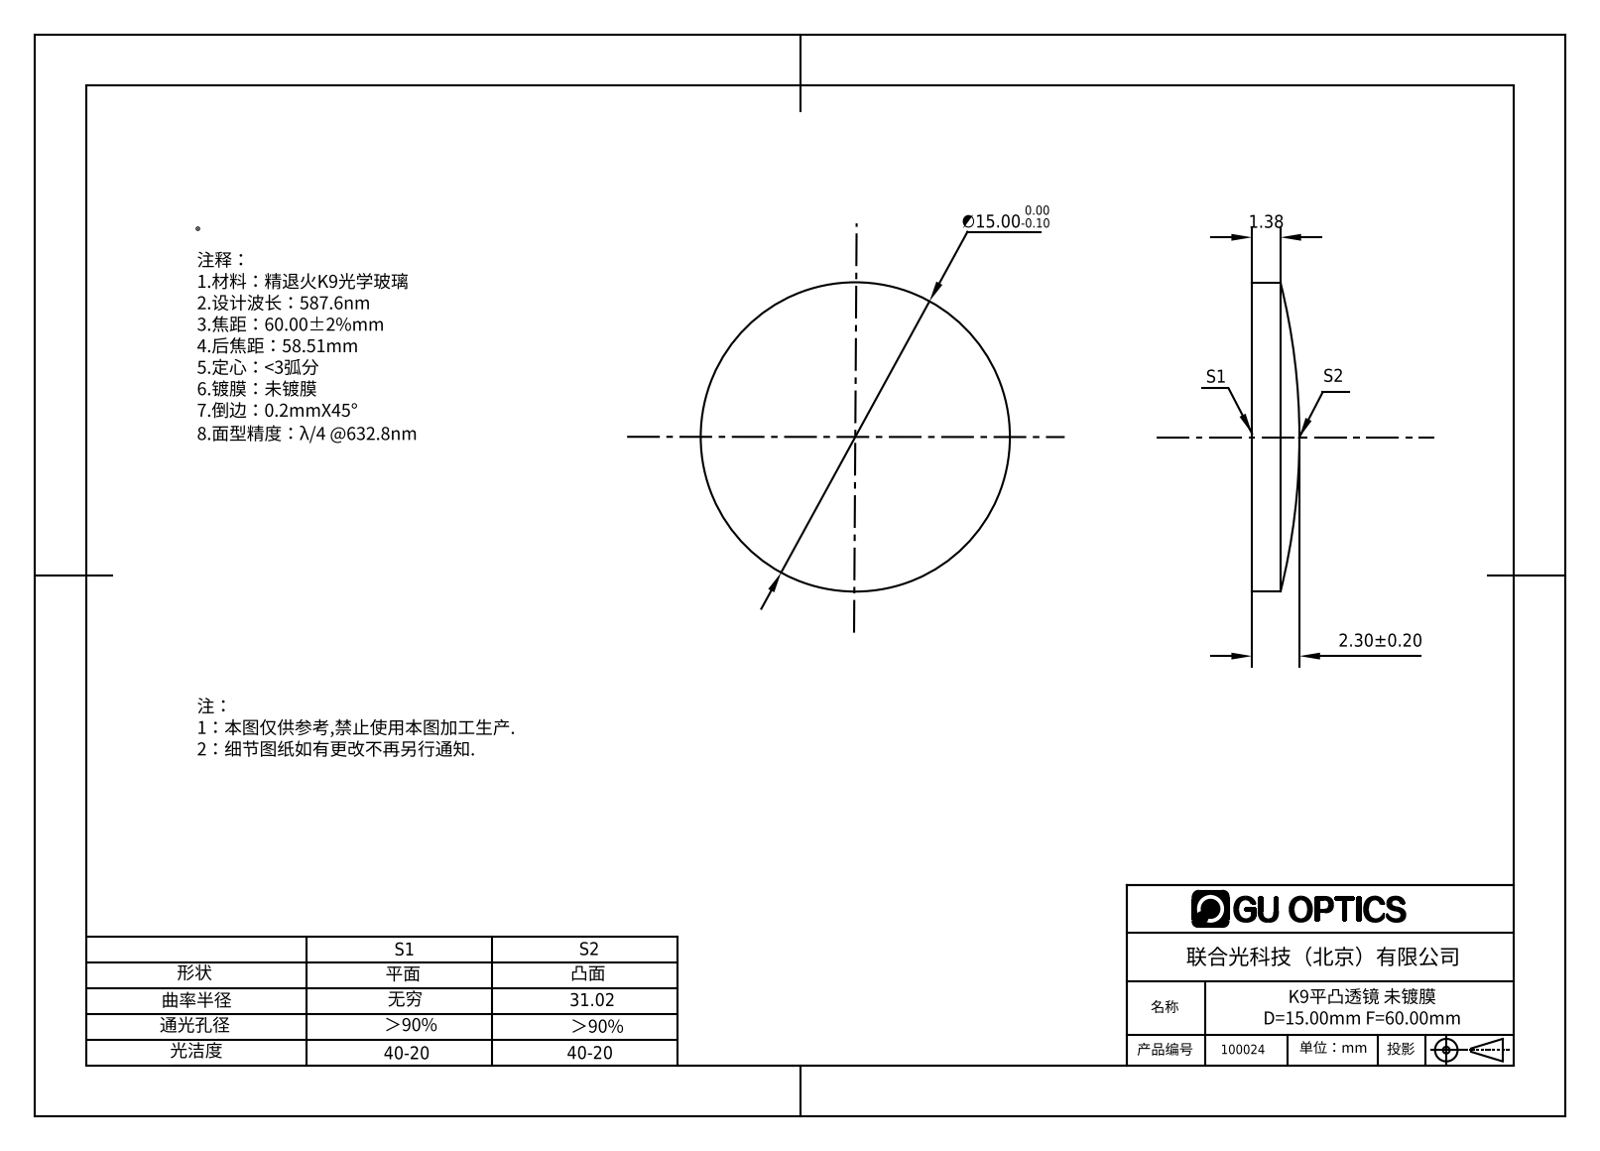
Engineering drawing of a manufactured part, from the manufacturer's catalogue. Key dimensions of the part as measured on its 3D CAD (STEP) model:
Part name (STEP PRODUCT): 100024
STEP written by: SolidWorks 2016 (AUTOMOTIVE_DESIGN)
Units: millimetres
Bodies: 1 solid, 5 faces (1 planar, 2 cylindrical, 2 other)
Overall size (bounding box): 15 × 15 × 2.3
Volume: 326 mm³ · Surface area: 421 mm²
Round bosses / shafts (diameter × count): ⌀15 ×1
